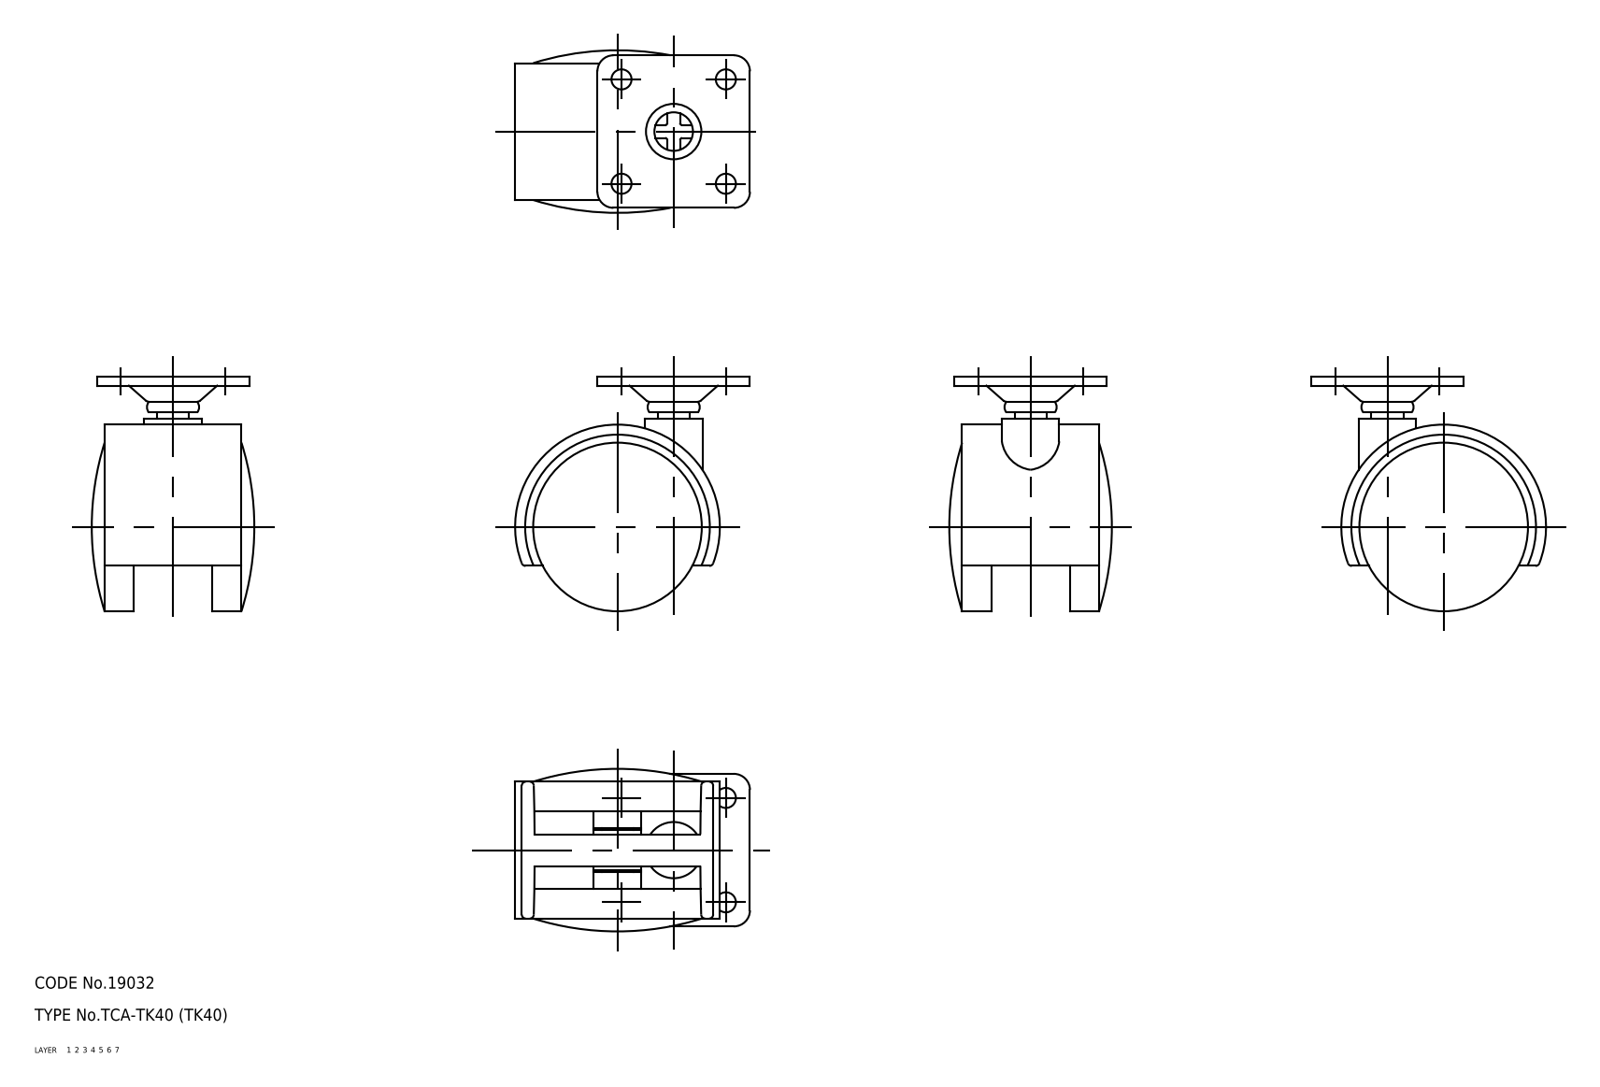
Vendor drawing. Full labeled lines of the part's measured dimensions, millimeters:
Part name (STEP PRODUCT): wheel; mounting plate; main shaft; TK40_3863_36
STEP written by: CADfix (AUTOMOTIVE_DESIGN)
Units: millimetres
Bodies: 5 solids, 130 faces (0 planar, 0 cylindrical, 130 other)
Overall size (bounding box): 58.5 × 58.5 × 40.5
Volume: 38 568 mm³ · Surface area: 24 879 mm²
